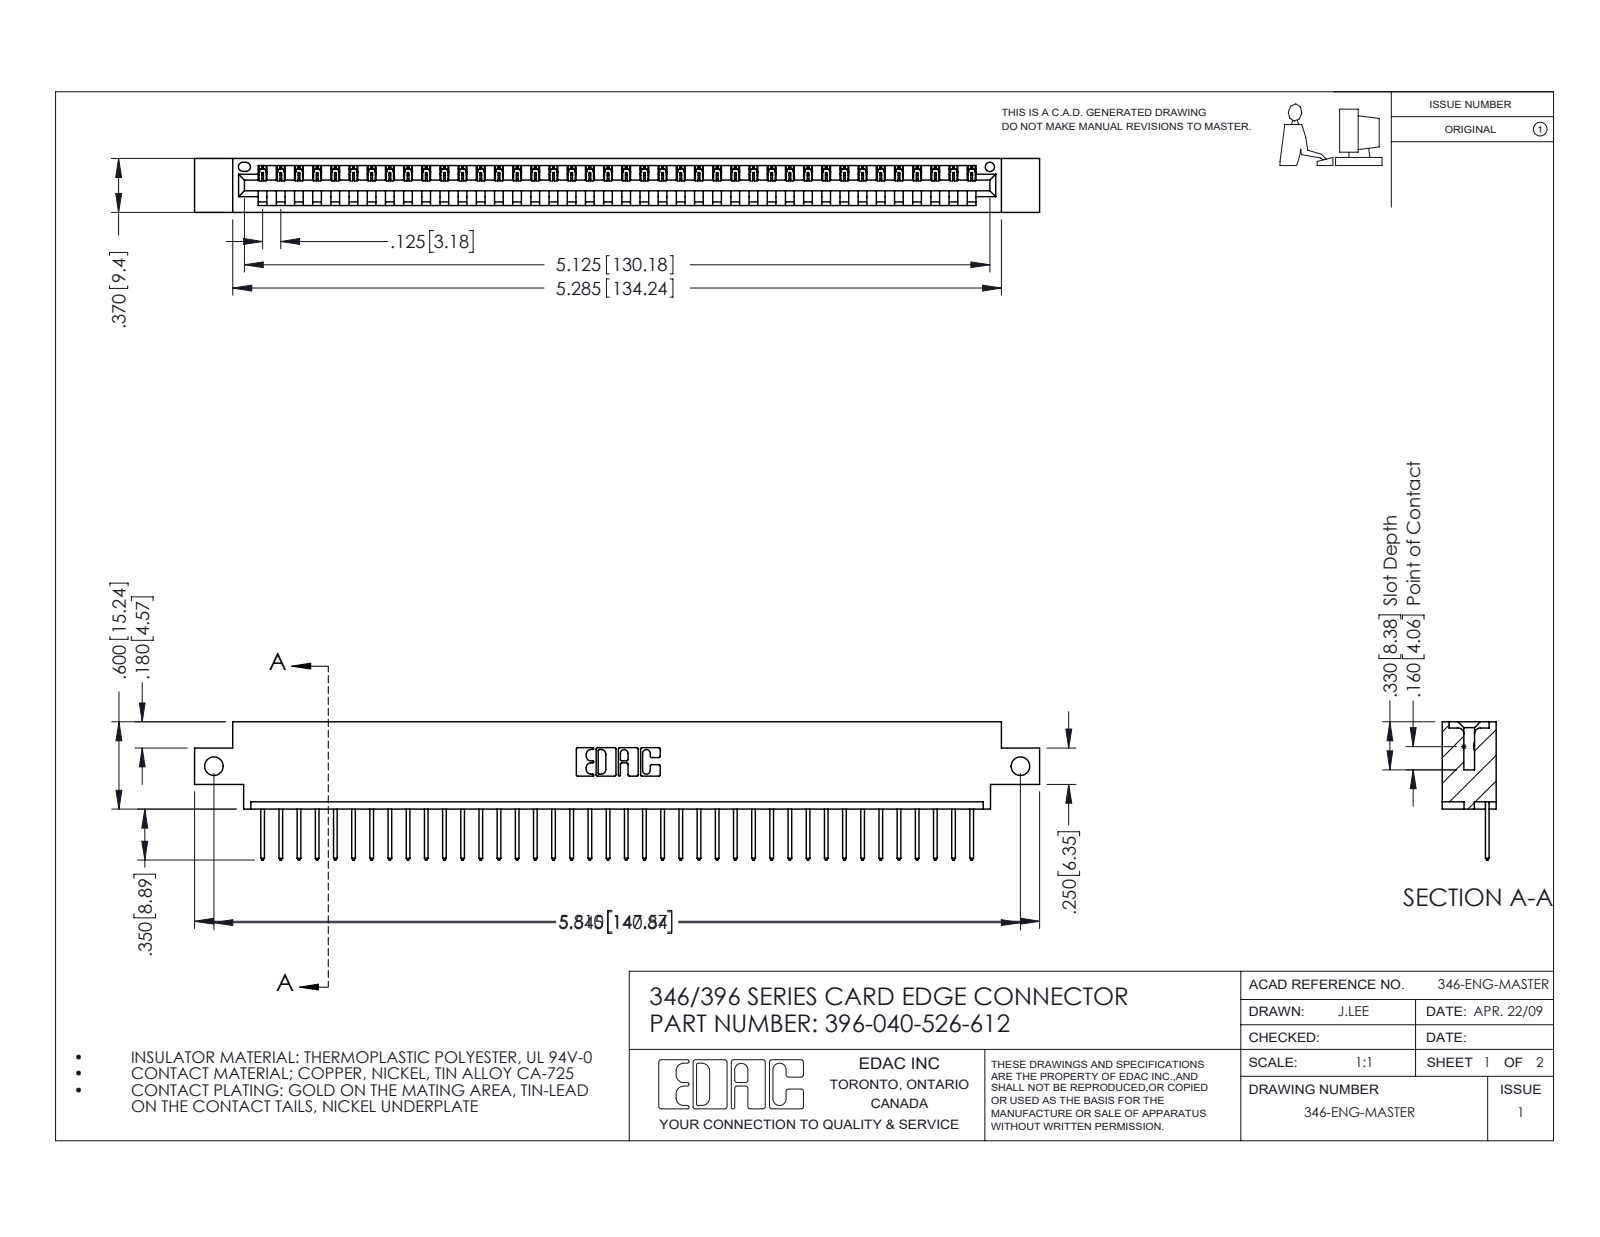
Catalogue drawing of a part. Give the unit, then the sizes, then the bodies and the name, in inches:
Units: inches
Overall size (bounding box): 5.81 × 0.95 × 0.37
Round holes (diameter × count): ⌀0.128 ×2, ⌀0.064 ×1
Partial cylindrical surfaces — rounded edges, fillets, slot ends (radius × count): R0.006 ×80, R0.01 ×80, R0.01 ×22, R0.007 ×6, R0.031 ×6, R0.026 ×3, R0.031 ×2, R0.04 ×2
Main face-to-face distances: 0.048, 0.322, 0.37, 0.25, 0.072, 0.298, 0.025, 0.148, 0.222, 0.1
Hole centre spacings: 5.545
Volume: 0.844 in³ · Surface area: 26.74 in²
Bodies: 41 solids, 2446 faces (1680 planar, 766 cylindrical, 0 other)
Part name (STEP PRODUCT): 345-292-001_345-293-126; 346 Part_0.170 Offset - Side Mount; 396-040-526-612
STEP written by: SolidWorks 2016 (CONFIG_CONTROL_DESIGN)
